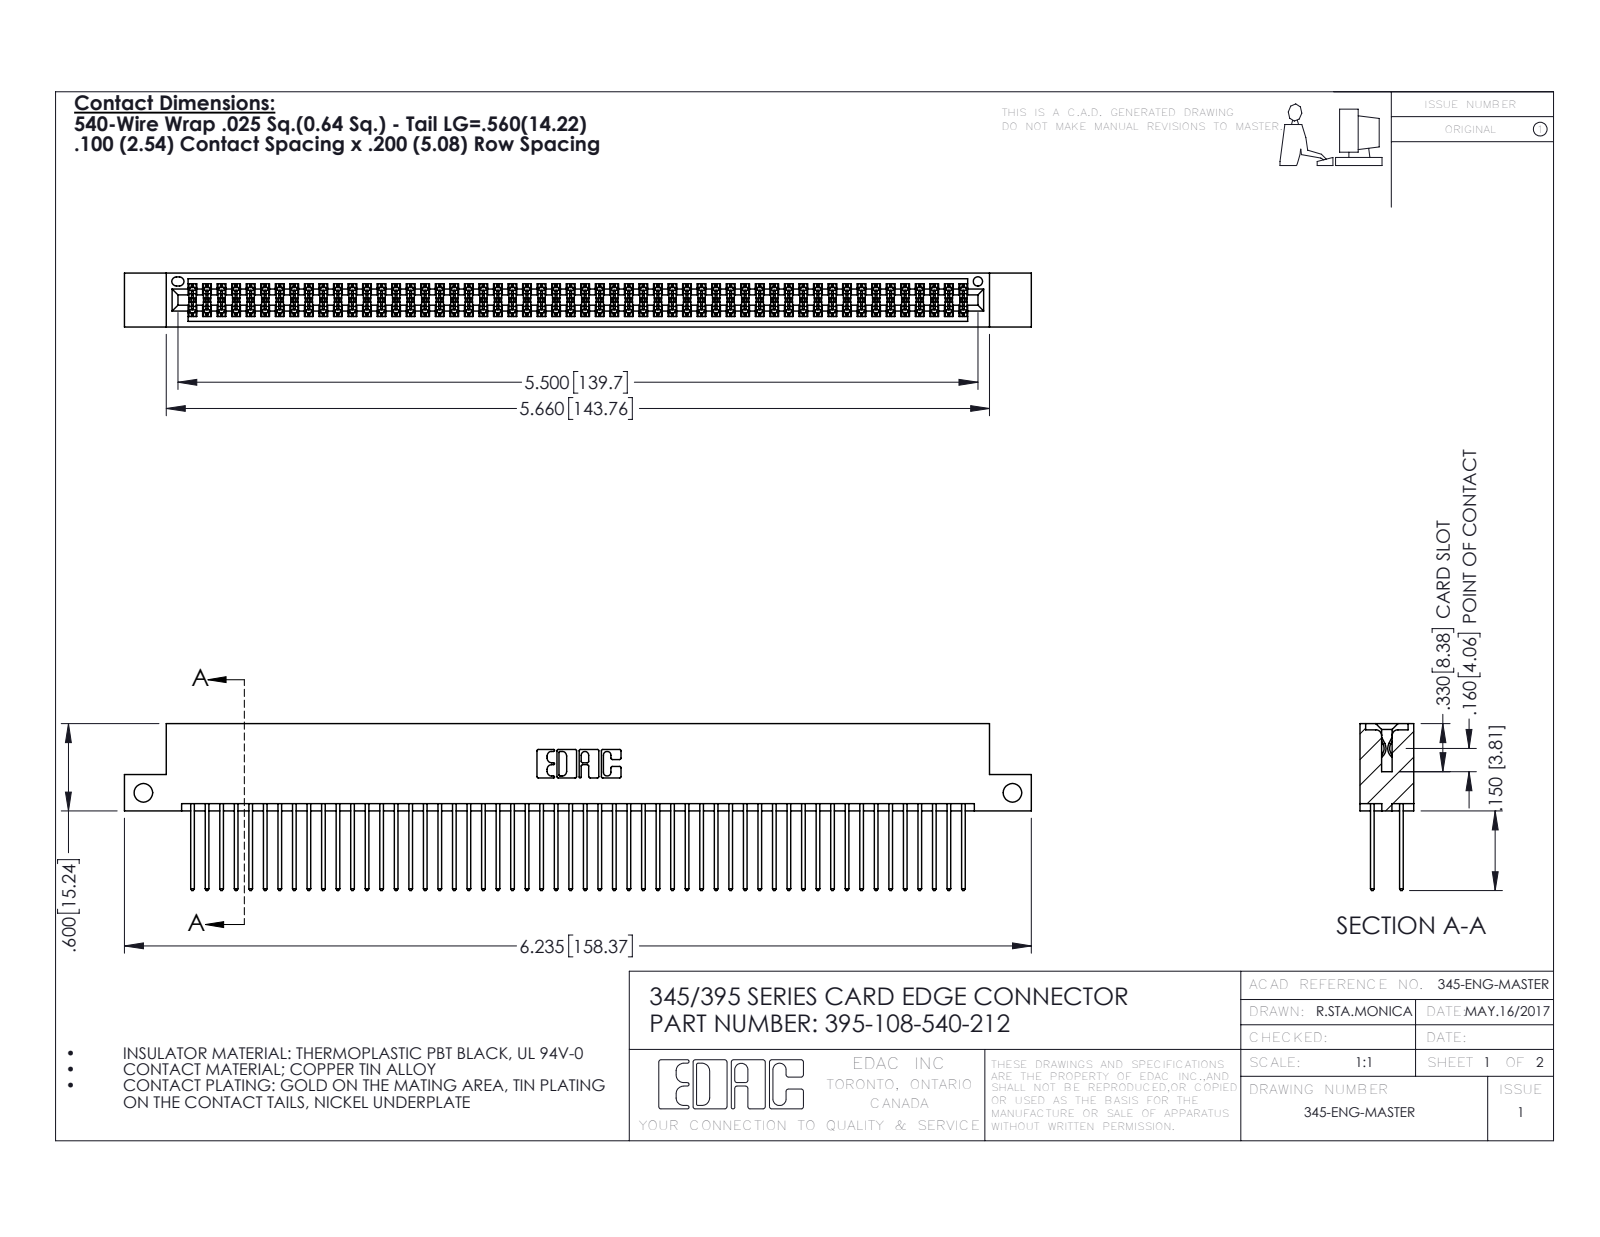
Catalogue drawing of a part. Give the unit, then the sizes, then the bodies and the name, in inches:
Units: inches
Overall size (bounding box): 6.235 × 1.147 × 0.37
Round holes (diameter × count): ⌀0.128 ×2, ⌀0.064 ×1
Partial cylindrical surfaces — rounded edges, fillets, slot ends (radius × count): R0.006 ×162, R0.01 ×108, R0.01 ×22, R0.007 ×6, R0.031 ×6, R0.026 ×3, R0.014 ×2, R0.019 ×2
Main face-to-face distances: 0.298, 0.072, 0.2, 0.098, 0.272, 0.025, 0.37, 0.225, 0.175, 0.149
Hole centre spacings: 5.975
Volume: 0.965 in³ · Surface area: 39.34 in²
Bodies: 109 solids, 5526 faces (3644 planar, 1882 cylindrical, 0 other)
Part name (STEP PRODUCT): 395-108-540-212; 345 Part_Flush Mounting Lugs - Side Mount; 345-292-001_345-293-140
STEP written by: SolidWorks 2016 (CONFIG_CONTROL_DESIGN)
